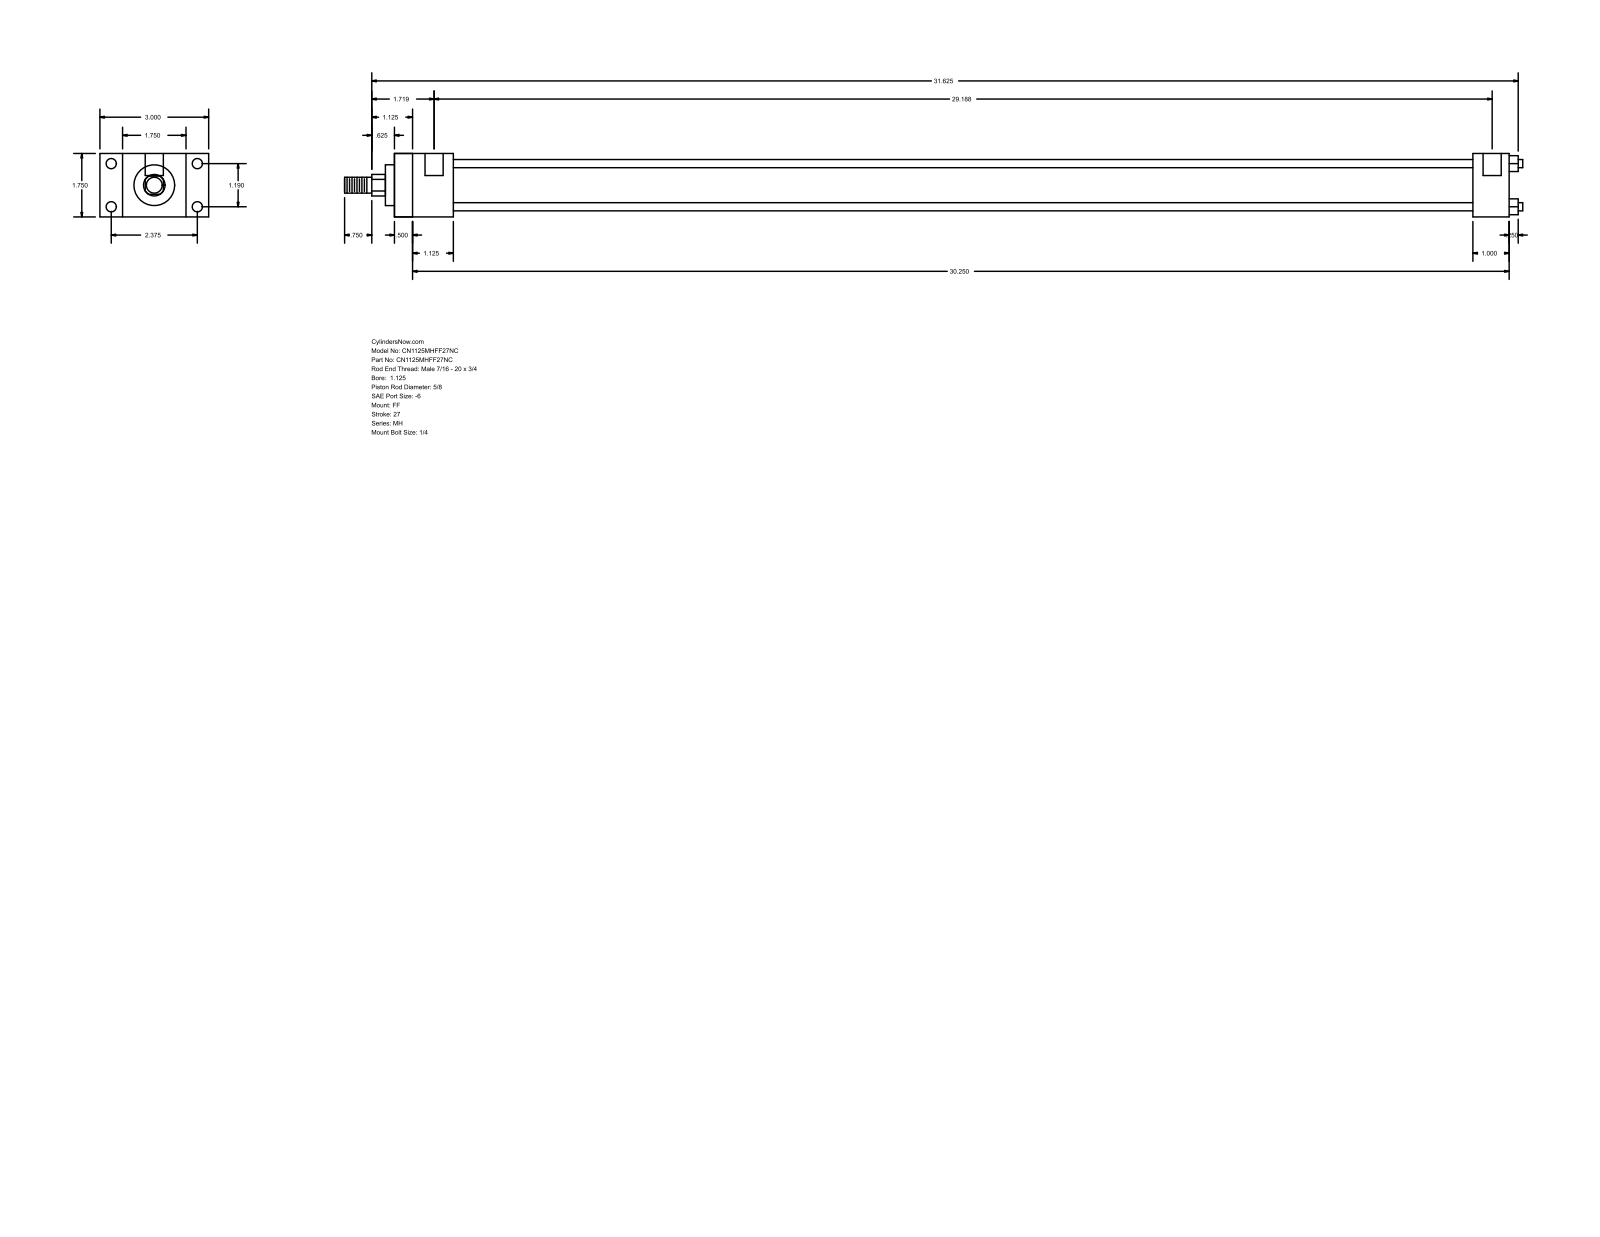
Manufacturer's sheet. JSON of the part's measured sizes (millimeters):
{"part_name": "MH_FF__0112_0.625", "step_written_by": "GSSL Pune (CONFIG_CONTROL_DESIGN)", "units": "millimeters", "bodies": {"solids": 0, "faces": 92, "planar": 64, "cylindrical": 28, "other": 0}, "overall_size": [825.5, 76.2, 44.45], "round_holes": [[5.56, 4], [7.14, 4], [12.7, 2]], "round_bosses_or_shafts": [[5.71, 4], [34.92, 1], [28.57, 1], [15.88, 1], [11.11, 1]], "partial_cylinders_radius": [[7.54, 1]], "face_to_face_distances": [44.46, 781.04, 15.87, 12.69, 768.35, 28.58, 60.33, 25.4, 41.27, 755.64], "hole_center_spacings": [30.22, 60.32, 67.47, 738.19, 3.17, 741.36]}
